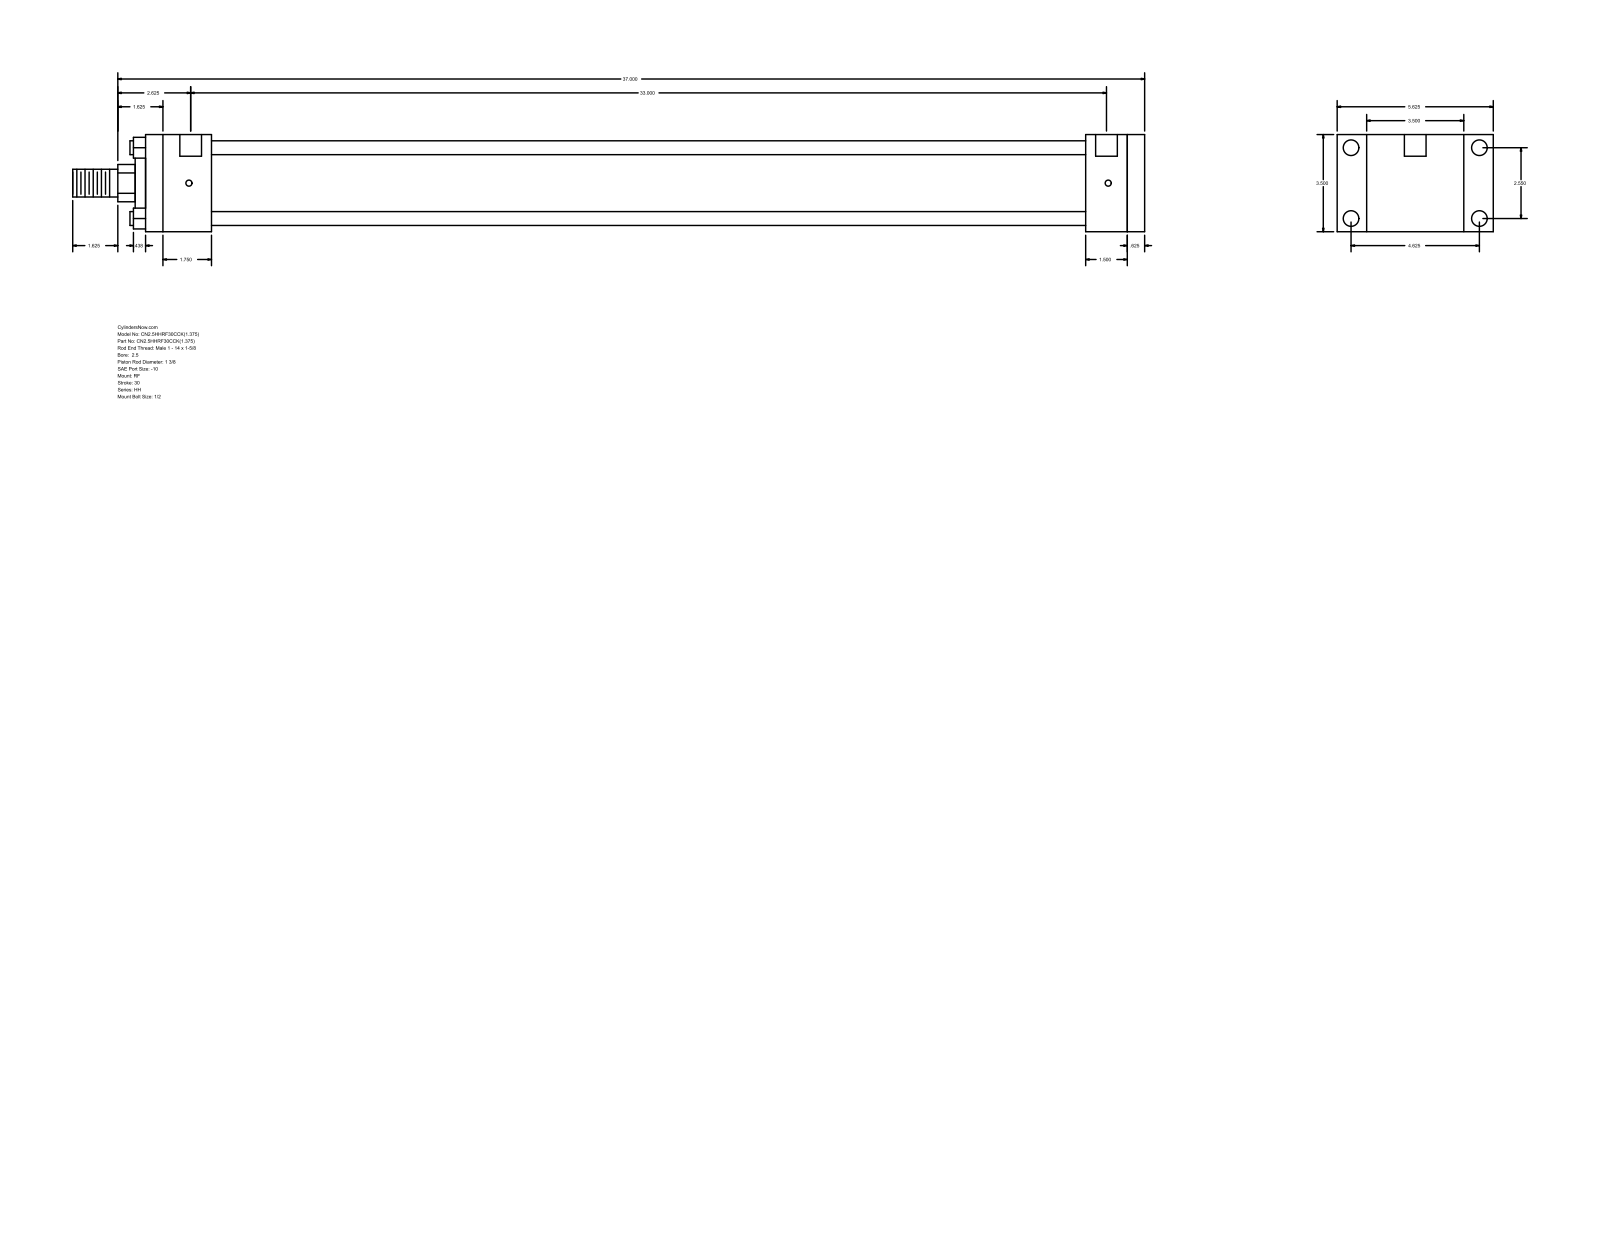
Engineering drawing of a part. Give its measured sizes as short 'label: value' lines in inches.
name: HH_RF__0250_1.375
written by: GSSL Pune (CONFIG_CONTROL_DESIGN)
unit: in
bodies: 0 solids, 92 faces (64 planar, 28 cylindrical, 0 other)
size: 38.625 × 5.625 × 3.5
holes: 4× ⌀0.219, 4× ⌀0.563, 2× ⌀0.781
bosses: 4× ⌀0.5, 1× ⌀2.875, 1× ⌀2, 1× ⌀1.375, 1× ⌀1
rounds: 1× R0.672
face distances: 3.5, 36, 0.625, 35.375, 2.125, 2.375, 33, 33.625, 33.875, 31.5
hole spacings: 0.062, 2.55, 4.625, 5.281, 33.063, 33.125, 33
